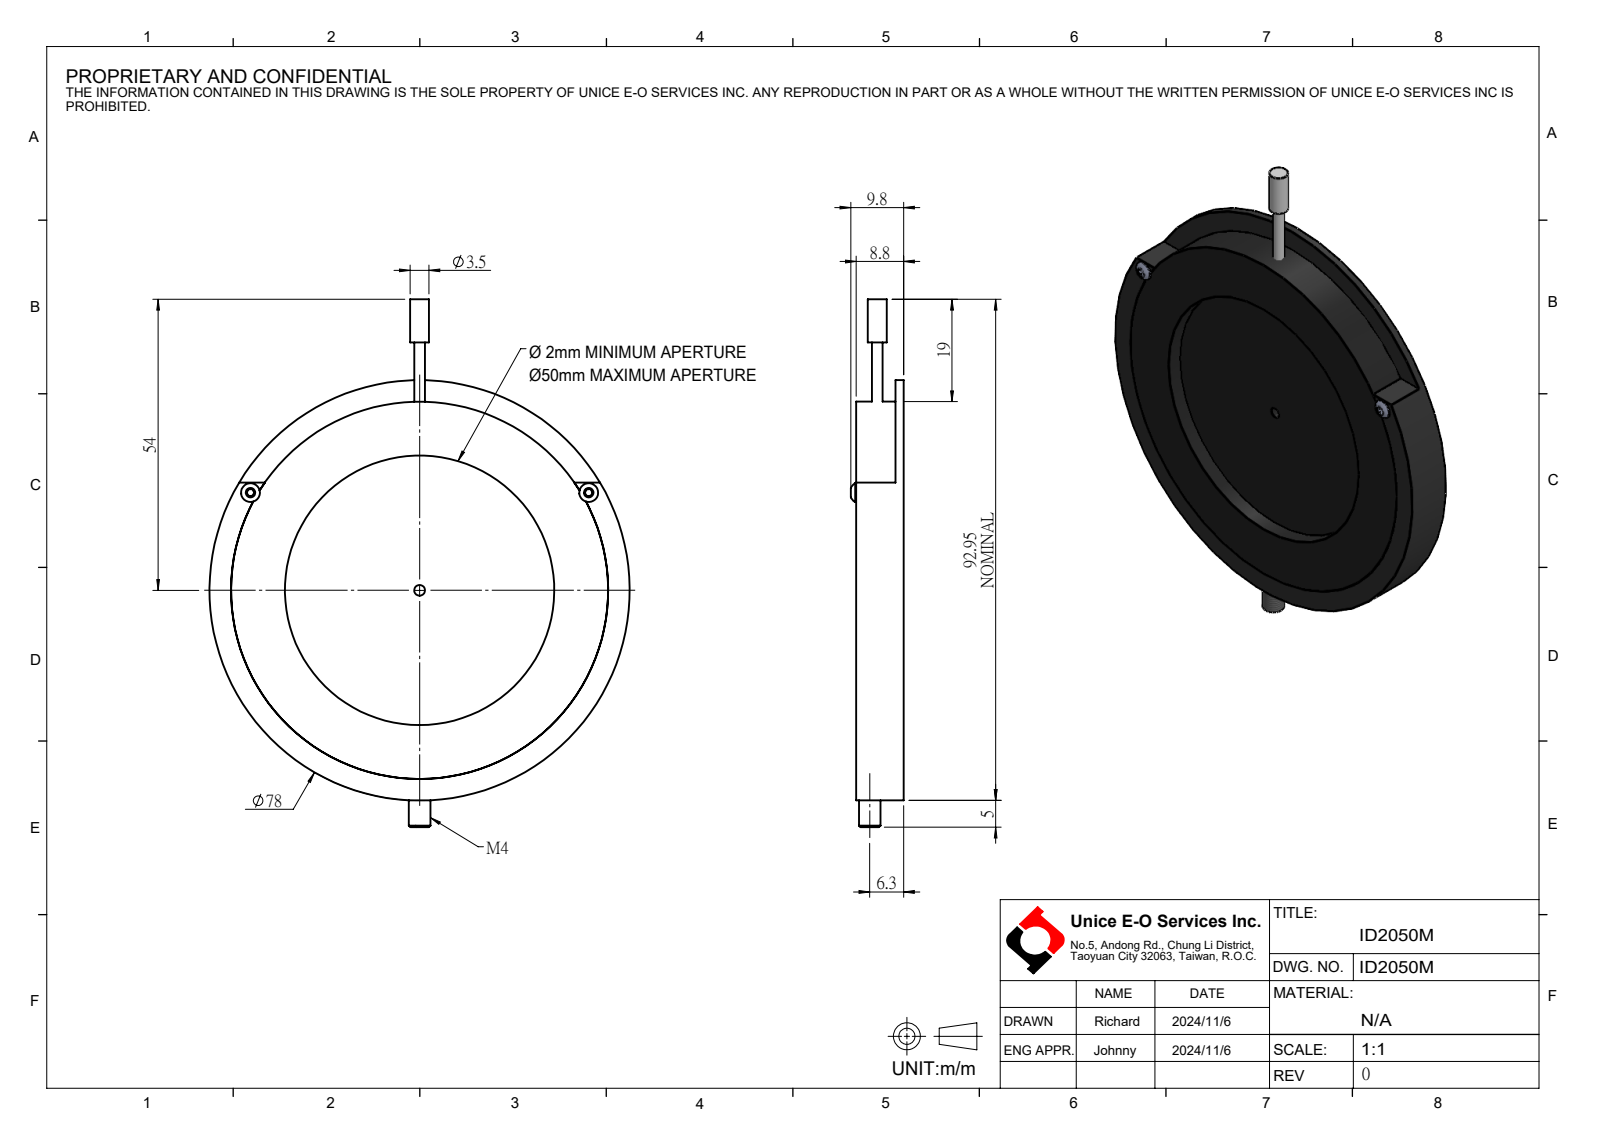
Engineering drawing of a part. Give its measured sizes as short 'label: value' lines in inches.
name: ID2050M; U-F1-ID2050M1-D0; U-F3-E2-M4x8_U-F3-E1-M5x6; ID2050 (+1 more)
written by: SolidWorks 2024 (AUTOMOTIVE_DESIGN)
unit: in
bodies: 6 solids, 91 faces (44 planar, 35 cylindrical, 12 other)
size: 3.856 × 3.071 × 0.386
volume: 1.513 in³; area: 25.53 in²
holes: 2× ⌀0.063, 1× ⌀0.079, 1× ⌀0.13, 1× ⌀1.969, 1× ⌀2.638, 1× ⌀2.756
bosses: 3× ⌀0.138, 3× ⌀0.079, 1× ⌀3.071, 1× ⌀0.157
face distances: 0.118, 0.189, 0.307, 0.071, 0.039, 0.157, 0.228, 0.346, 0.059, 0.02
hole spacings: 1.427, 2.472
